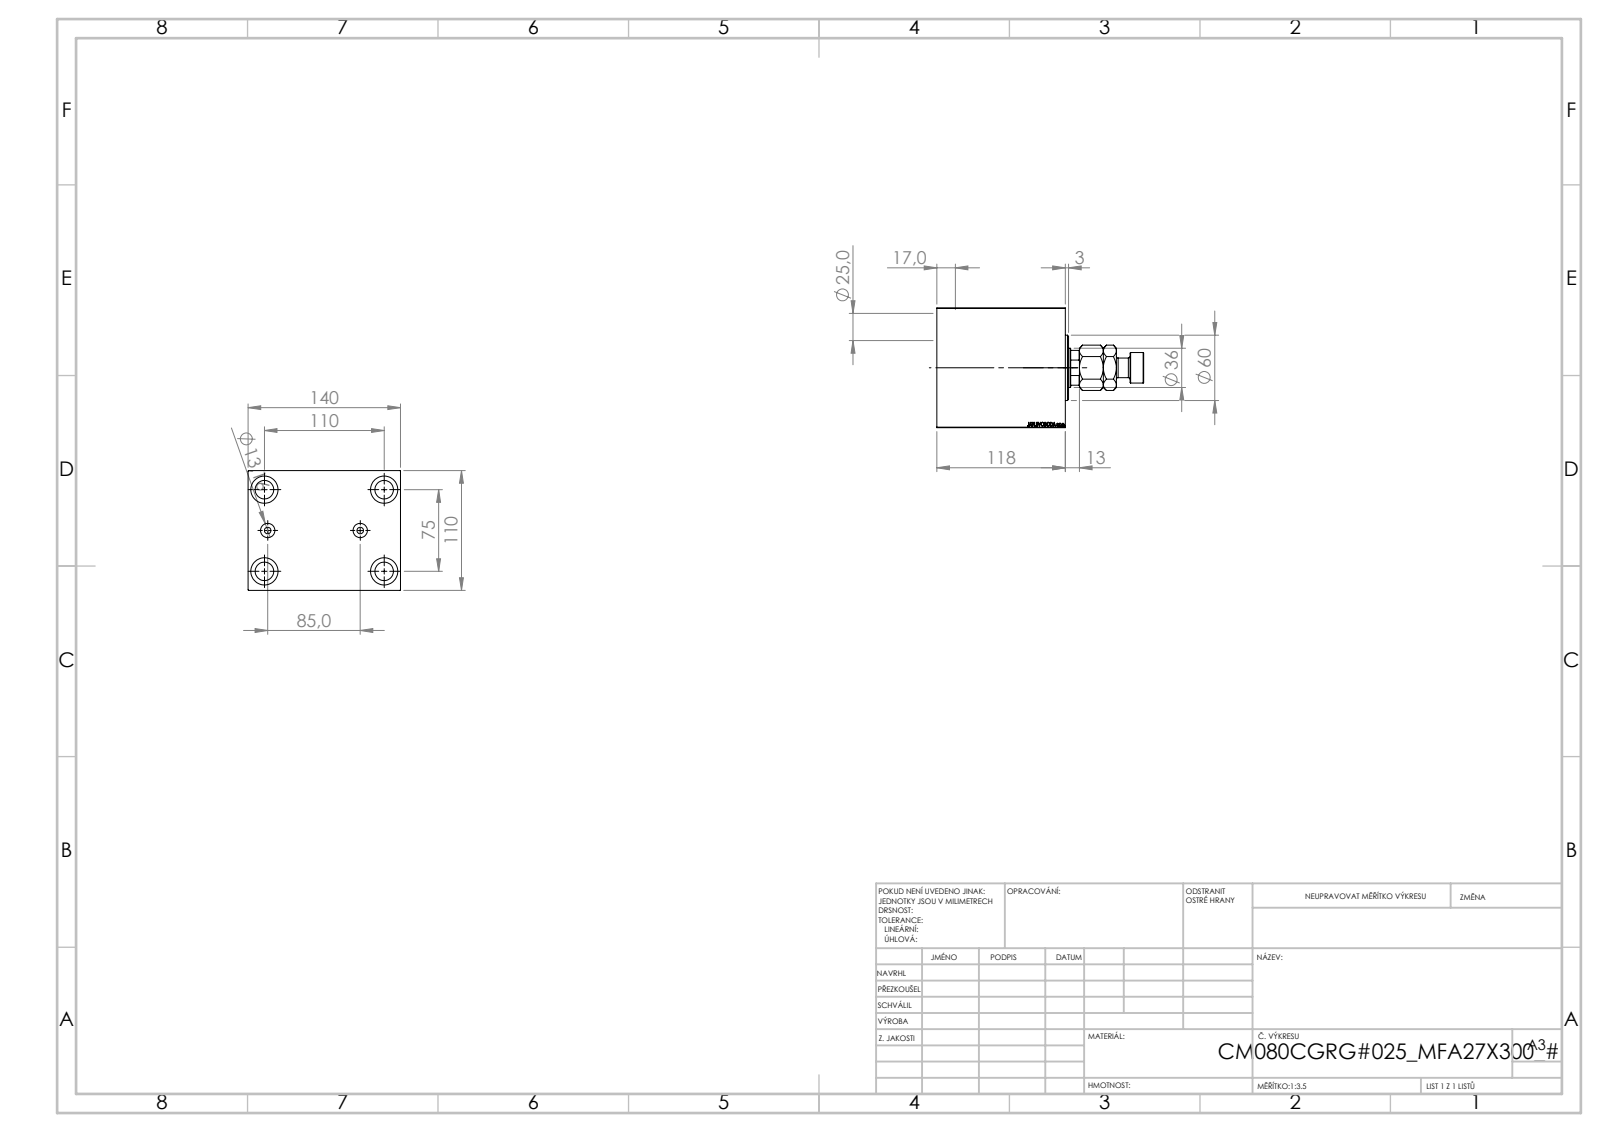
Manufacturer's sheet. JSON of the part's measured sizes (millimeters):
{"part_name": "V450CM_VC_B; V450CM_C_Body; V450CM_C_VCP; MFA", "step_written_by": "SolidWorks 2019 (CONFIG_CONTROL_DESIGN)", "units": "millimeters", "bodies": {"solids": 4, "faces": 915, "planar": 427, "cylindrical": 62, "other": 426}, "overall_size": [191, 140, 110], "volume_mm3": 1615000, "surface_area_mm2": 182973, "round_holes": [[17, 4], [25, 4], [6, 2], [13.16, 2], [25.5, 1], [36, 1], [39.5, 1], [80, 1], [82, 1], [87, 1]], "round_bosses_or_shafts": [[60, 1], [28, 1], [18, 1]], "partial_cylinders_radius": [[17.5, 1]], "face_to_face_distances": [110, 140, 118, 59.5, 58.5, 108, 83, 10, 25, 49.5], "hole_center_spacings": [39.53, 66.57, 104.46, 42.5, 75, 110, 133.14, 85]}
